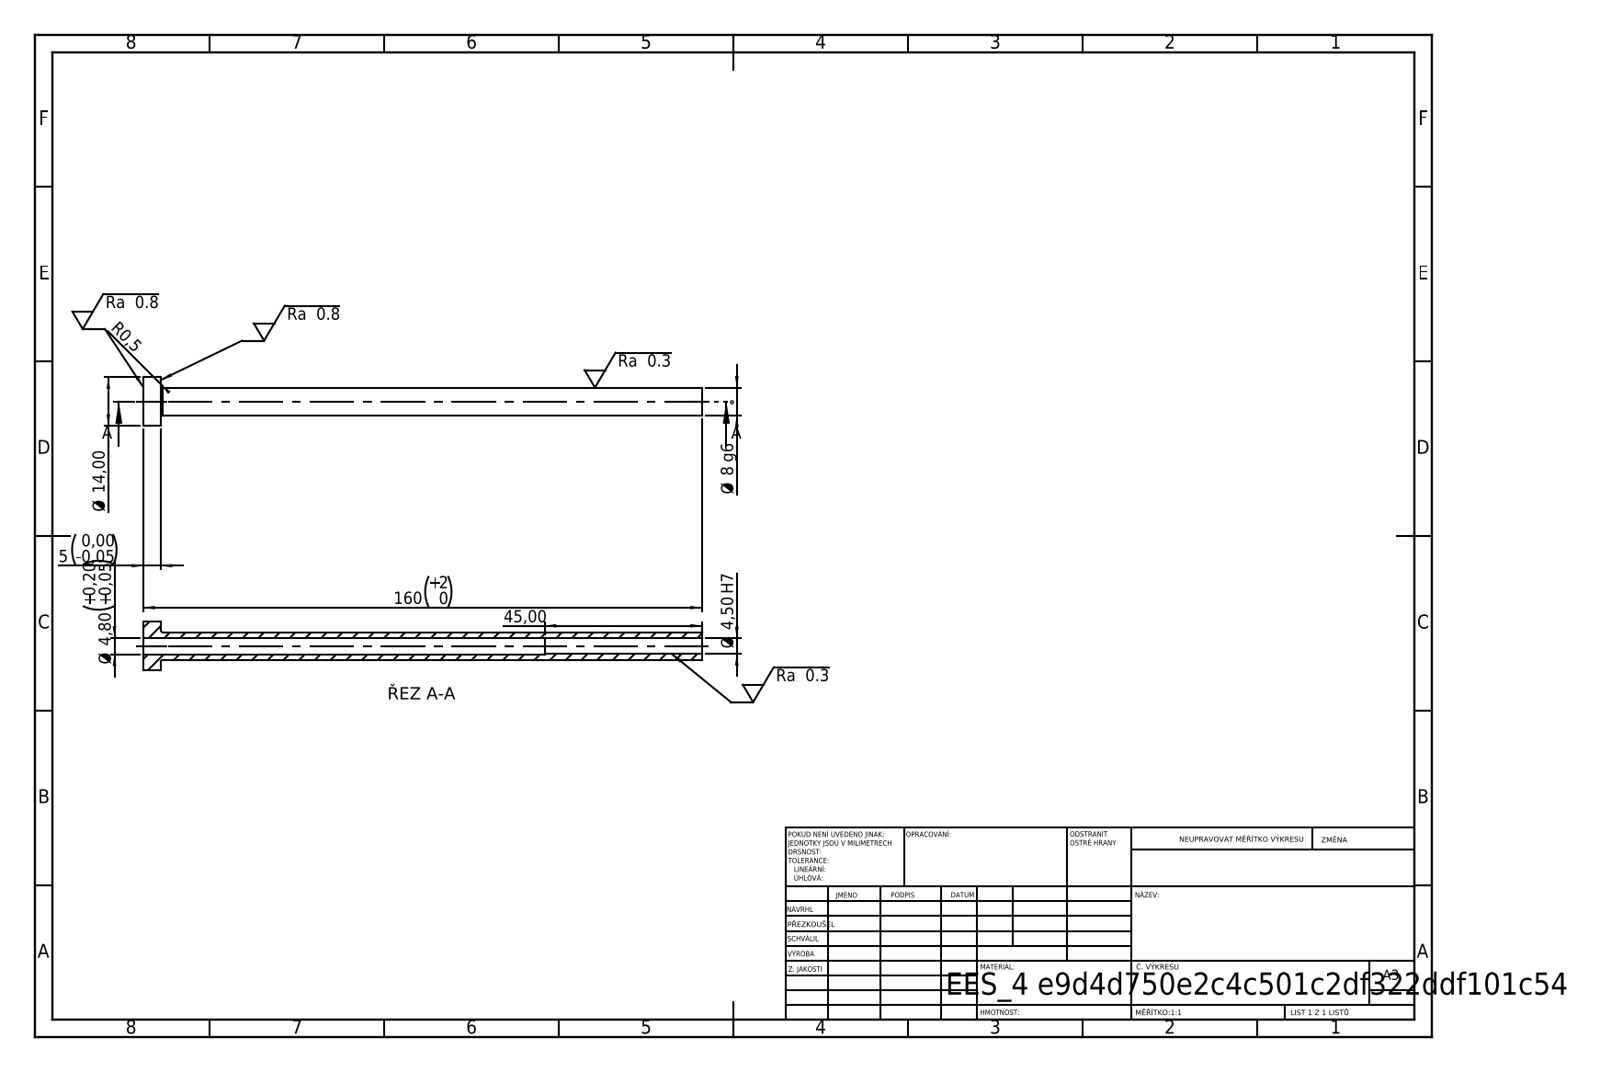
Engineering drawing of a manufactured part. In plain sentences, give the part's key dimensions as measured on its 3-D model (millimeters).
Its 3-D file was written by "SolidWorks 2019 (CONFIG_CONTROL_DESIGN)". It is 1 solid with 14 faces: 4 planar, 8 cylindrical and 2 other. Overall it measures 160 by 14 by 14 millimeters. Its volume is 5 766 cubic millimeters and its surface area 6 757 square millimeters. Round holes: 1 of diameter 4.5, 1 of diameter 4.8. Round bosses or shafts: 1 of diameter 14, 1 of diameter 8. The main face-to-face distances are 5, 160, 155, 115, 110, 45.
